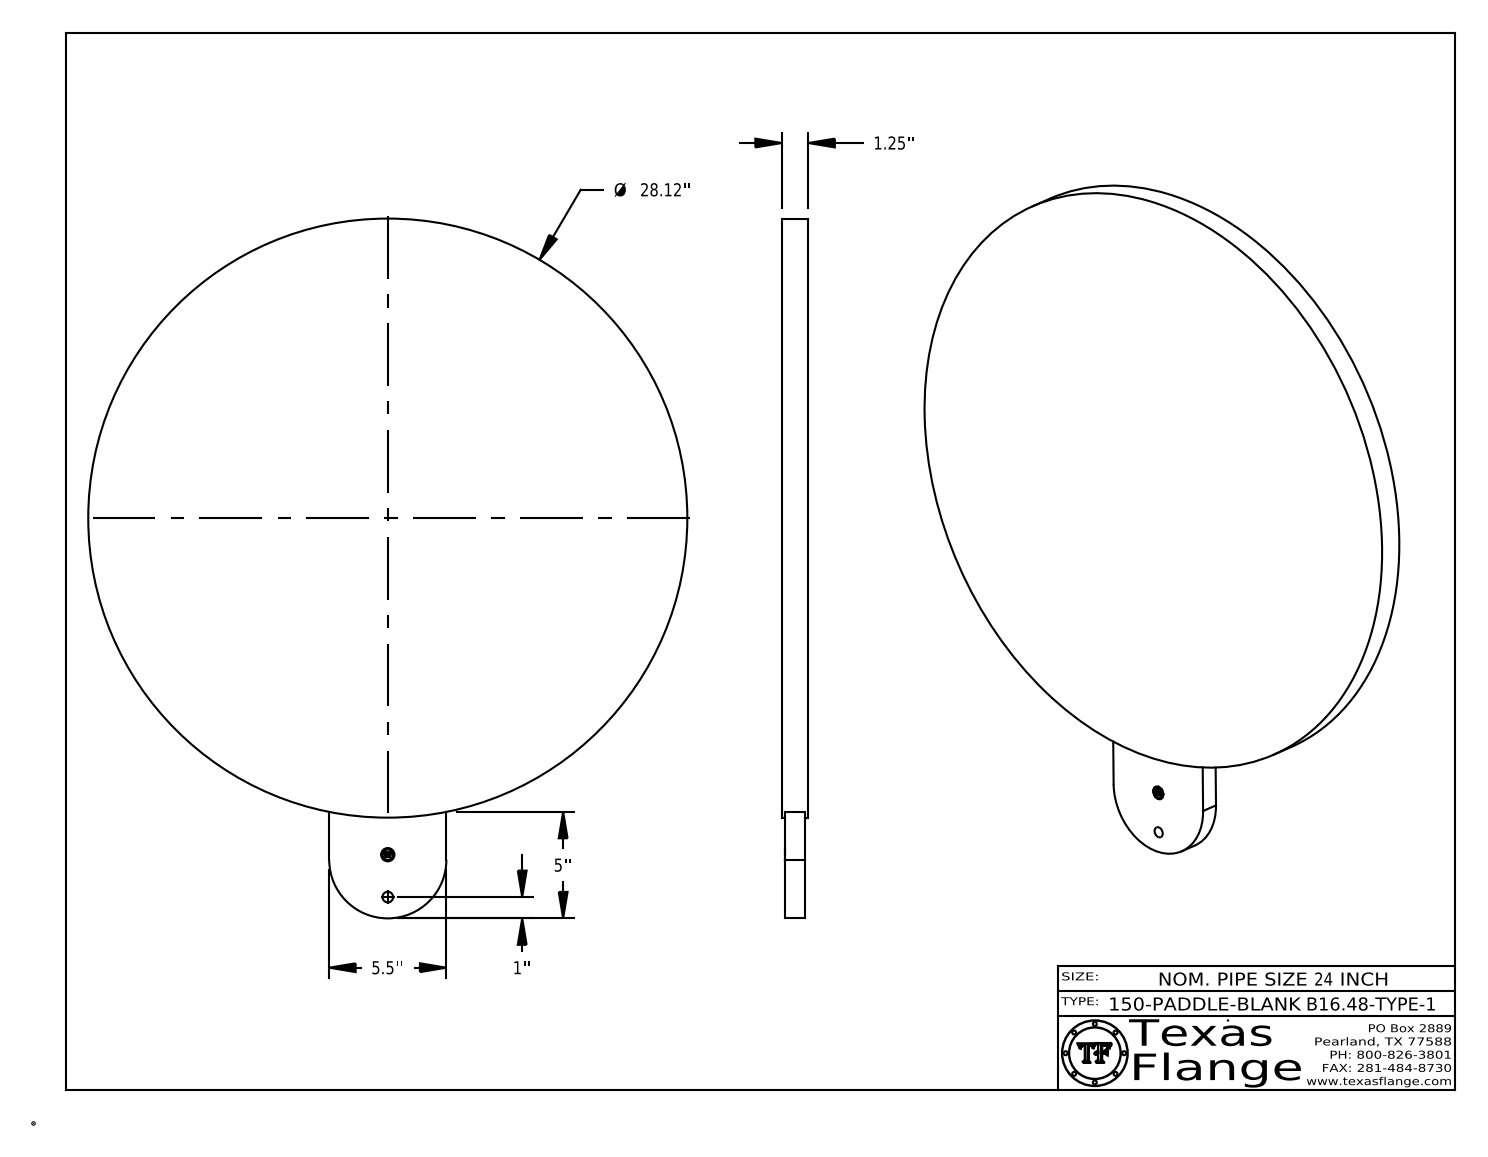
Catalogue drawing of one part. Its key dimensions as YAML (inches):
part_name: "24-150-PADDLE-BLANK-B16.48-TYPE-1"
step_written_by: "CATIA V5 STEP AP214 (AUTOMOTIVE_DESIGN)"
units: inches
bodies: {solids: 1, faces: 396, planar: 371, cylindrical: 25, other: 0}
overall_size: [32.848, 28.12, 1.25]
volume: 797.9
surface_area: 1407
round_holes:
  - {diameter: 0.5, count: 1}
  - {diameter: 0.625, count: 1}
round_bosses_or_shafts:
  - {diameter: 0.038, count: 8}
  - {diameter: 28.12, count: 1}
  - {diameter: 0.492, count: 1}
partial_cylinders:
  - {radius: 2.75, count: 1}
face_to_face_distances: [1.25, 0.156, 1.094, 0.938, 5.5, 1.079, 0.923, 0.015, 0.171, 2.687]
hole_center_spacings: [1.989]
